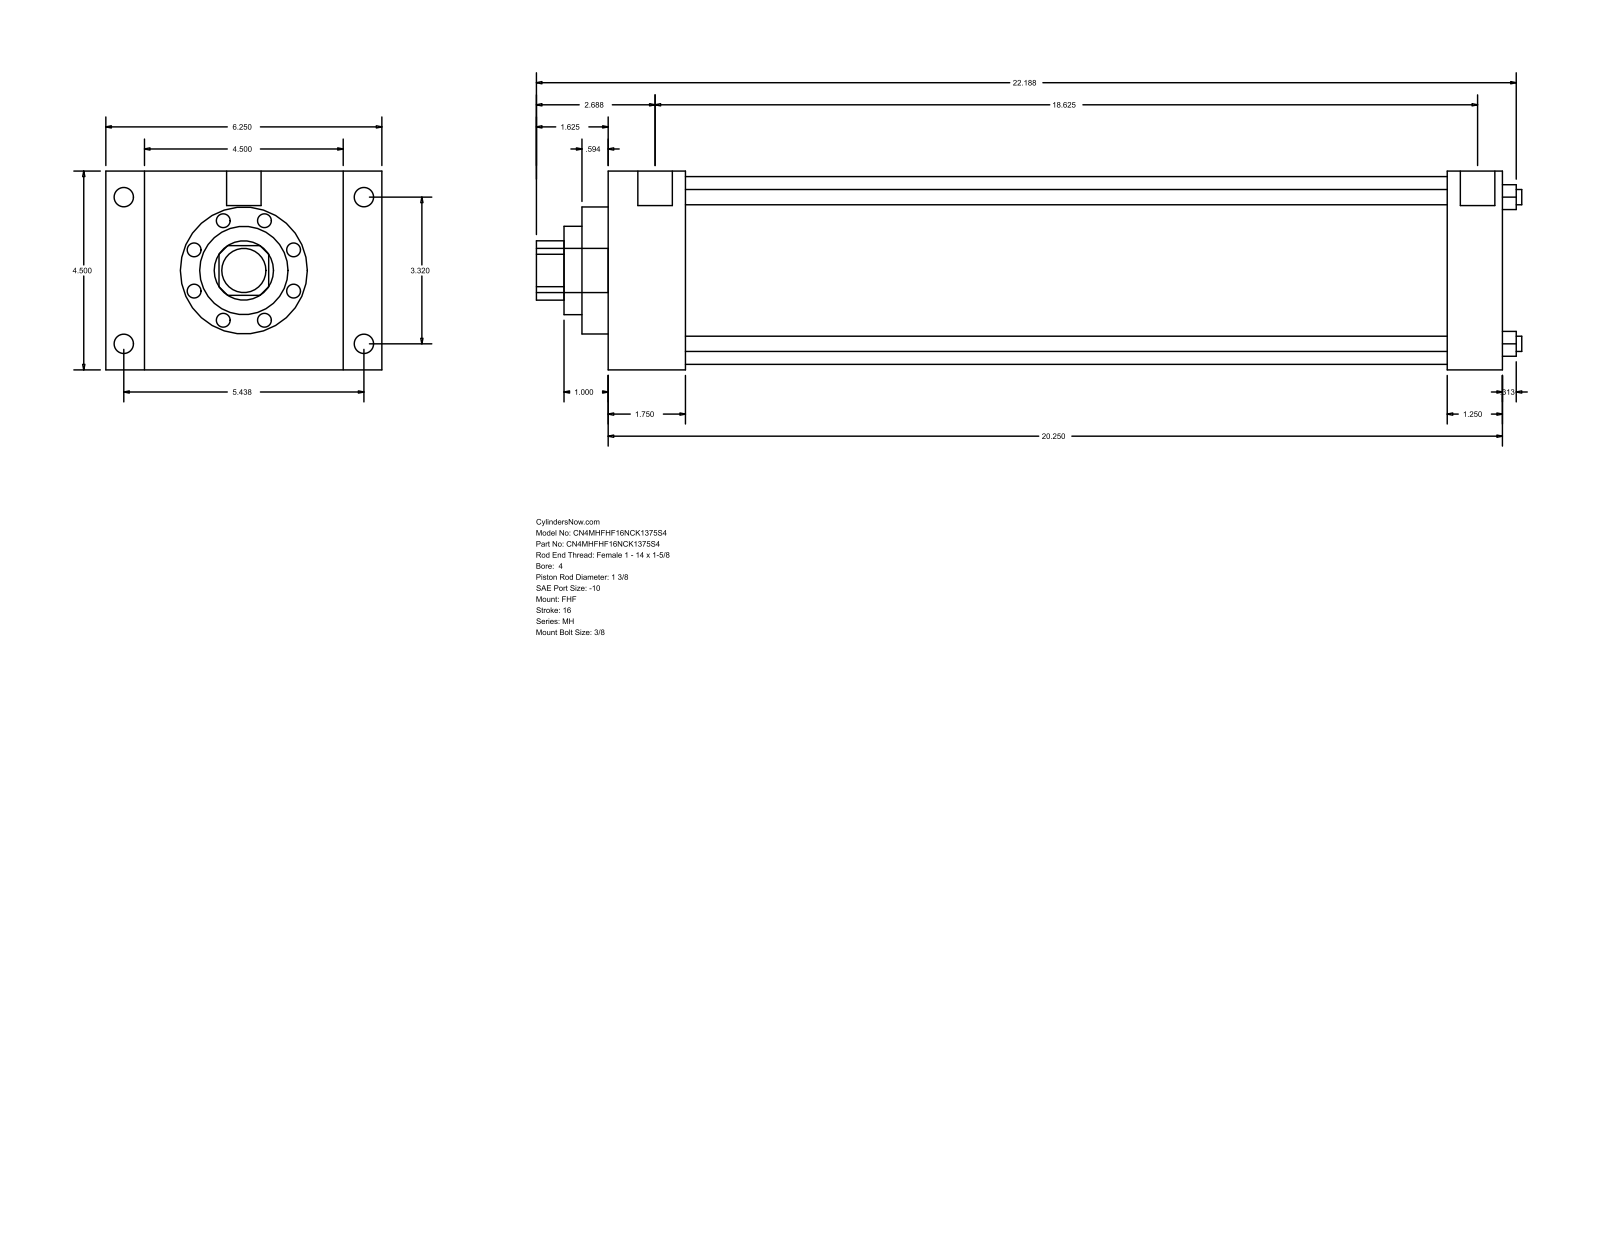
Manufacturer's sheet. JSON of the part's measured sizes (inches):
{"part_name": "MH_FHF__0400_1.375", "step_written_by": "GSSL Pune (CONFIG_CONTROL_DESIGN)", "units": "inches", "bodies": {"solids": 0, "faces": 90, "planar": 61, "cylindrical": 29, "other": 0}, "overall_size": [22.313, 6.25, 4.5], "round_holes": [[0.345, 4], [1.375, 1], [2, 1], [2.875, 1], [4.25, 1]], "round_bosses_or_shafts": [[0.438, 4], [0.344, 4], [0.781, 2], [1, 1]], "partial_cylinders_radius": [[0.672, 1]], "face_to_face_distances": [4.5, 20.25, 1.75, 18.5, 0.875, 5.375, 6.25, 19, 17.25, 1.25], "hole_center_spacings": [2.347, 3.32, 4.695]}
